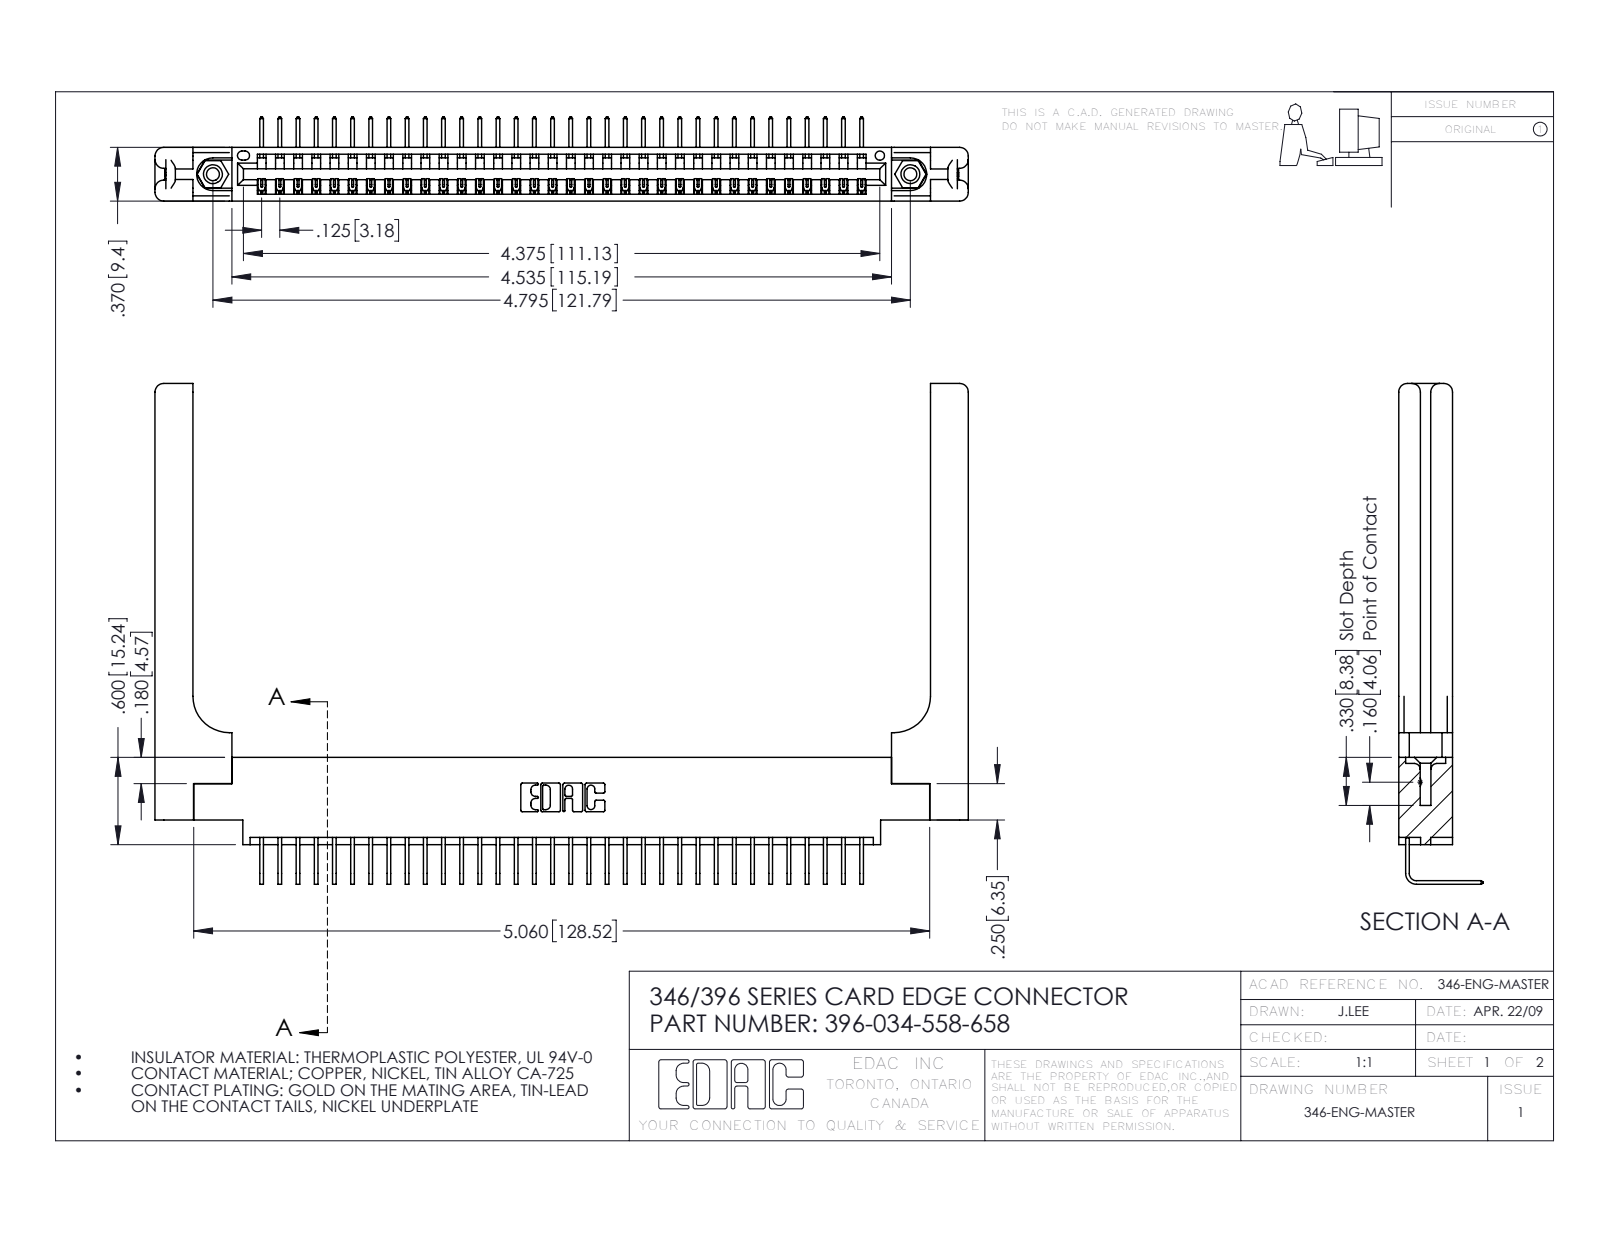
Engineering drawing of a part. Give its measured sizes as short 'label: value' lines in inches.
name: 345-250-001_345-250-001-102; 345-292-001_558 Tail - 2; 346-220-058_345-220-058; 346 Part_0.170 Offset - 0.156 Dia-TH (+1 more)
written by: SolidWorks 2016 (CONFIG_CONTROL_DESIGN)
unit: in
bodies: 39 solids, 2422 faces (1656 planar, 706 cylindrical, 60 other)
size: 5.591 × 3.443 × 0.58
volume: 1.282 in³; area: 35.32 in²
holes: 2× ⌀0.089, 2× ⌀0.125, 2× ⌀0.156, 1× ⌀0.064
bosses: 2× ⌀0.155
rounds: 68× R0.006, 22× R0.01, 16× R0.06, 6× R0.007, 6× R0.031, 3× R0.026, 2× R0.03, 2× R0.031
face distances: 0.37, 0.322, 0.048, 0.072, 0.148, 0.15, 0.025, 0.298, 0.25, 0.222
hole spacings: 0.246, 4.587, 4.795
